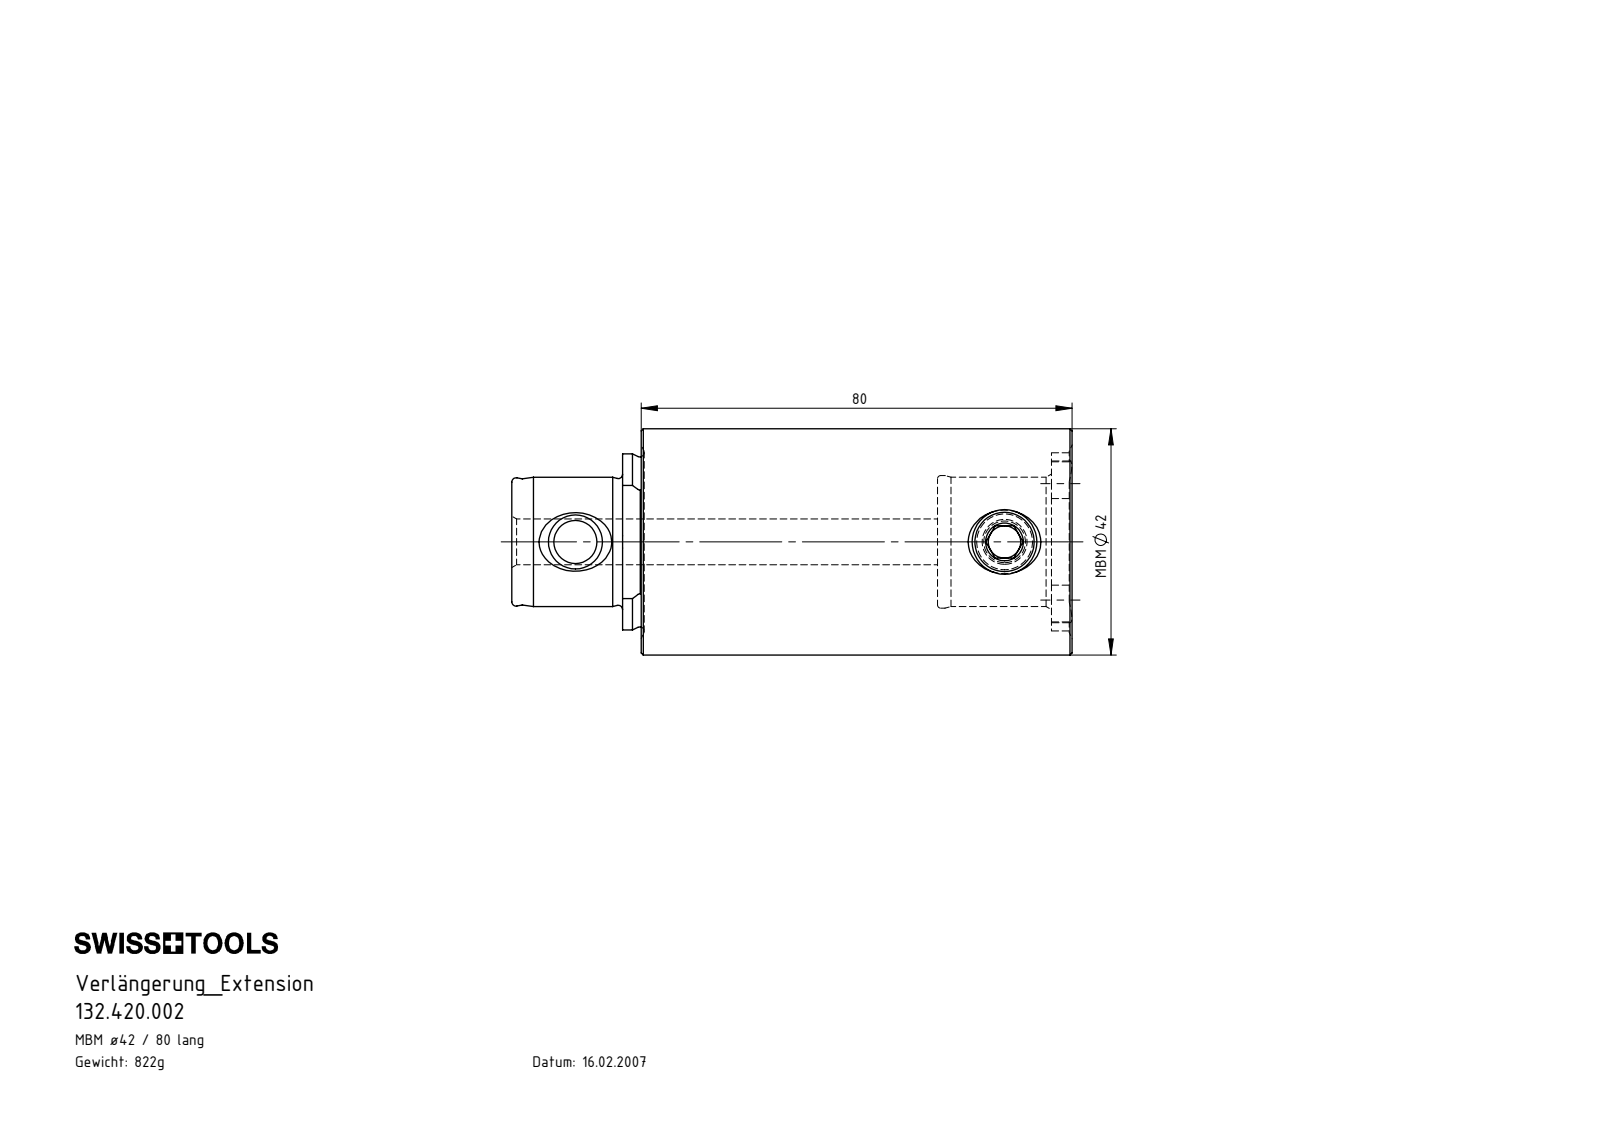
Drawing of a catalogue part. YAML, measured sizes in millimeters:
part_name: "MB4-ER1.001.013_A; MB4.MB4.K01.080; MB4-MB4.K01.080_B"
step_written_by: "SolidWorks 2012 (CONFIG_CONTROL_DESIGN)"
units: millimeters
bodies: {solids: 2, faces: 118, planar: 29, cylindrical: 30, other: 59}
overall_size: [104, 42, 42]
volume: 104671
surface_area: 20022
round_holes:
  - {diameter: 8, count: 1}
  - {diameter: 8.5, count: 1}
  - {diameter: 11, count: 1}
  - {diameter: 24, count: 1}
  - {diameter: 24.6, count: 1}
round_bosses_or_shafts:
  - {diameter: 42, count: 1}
  - {diameter: 12, count: 1}
partial_cylinders:
  - {radius: 4.2, count: 4}
  - {radius: 14.9, count: 1}
  - {radius: 16.32, count: 1}
  - {radius: 16.52, count: 1}
face_to_face_distances: [25, 21.15, 79.6, 79, 100.15, 24, 55, 76.15, 104, 80]
hole_center_spacings: [79.65]
